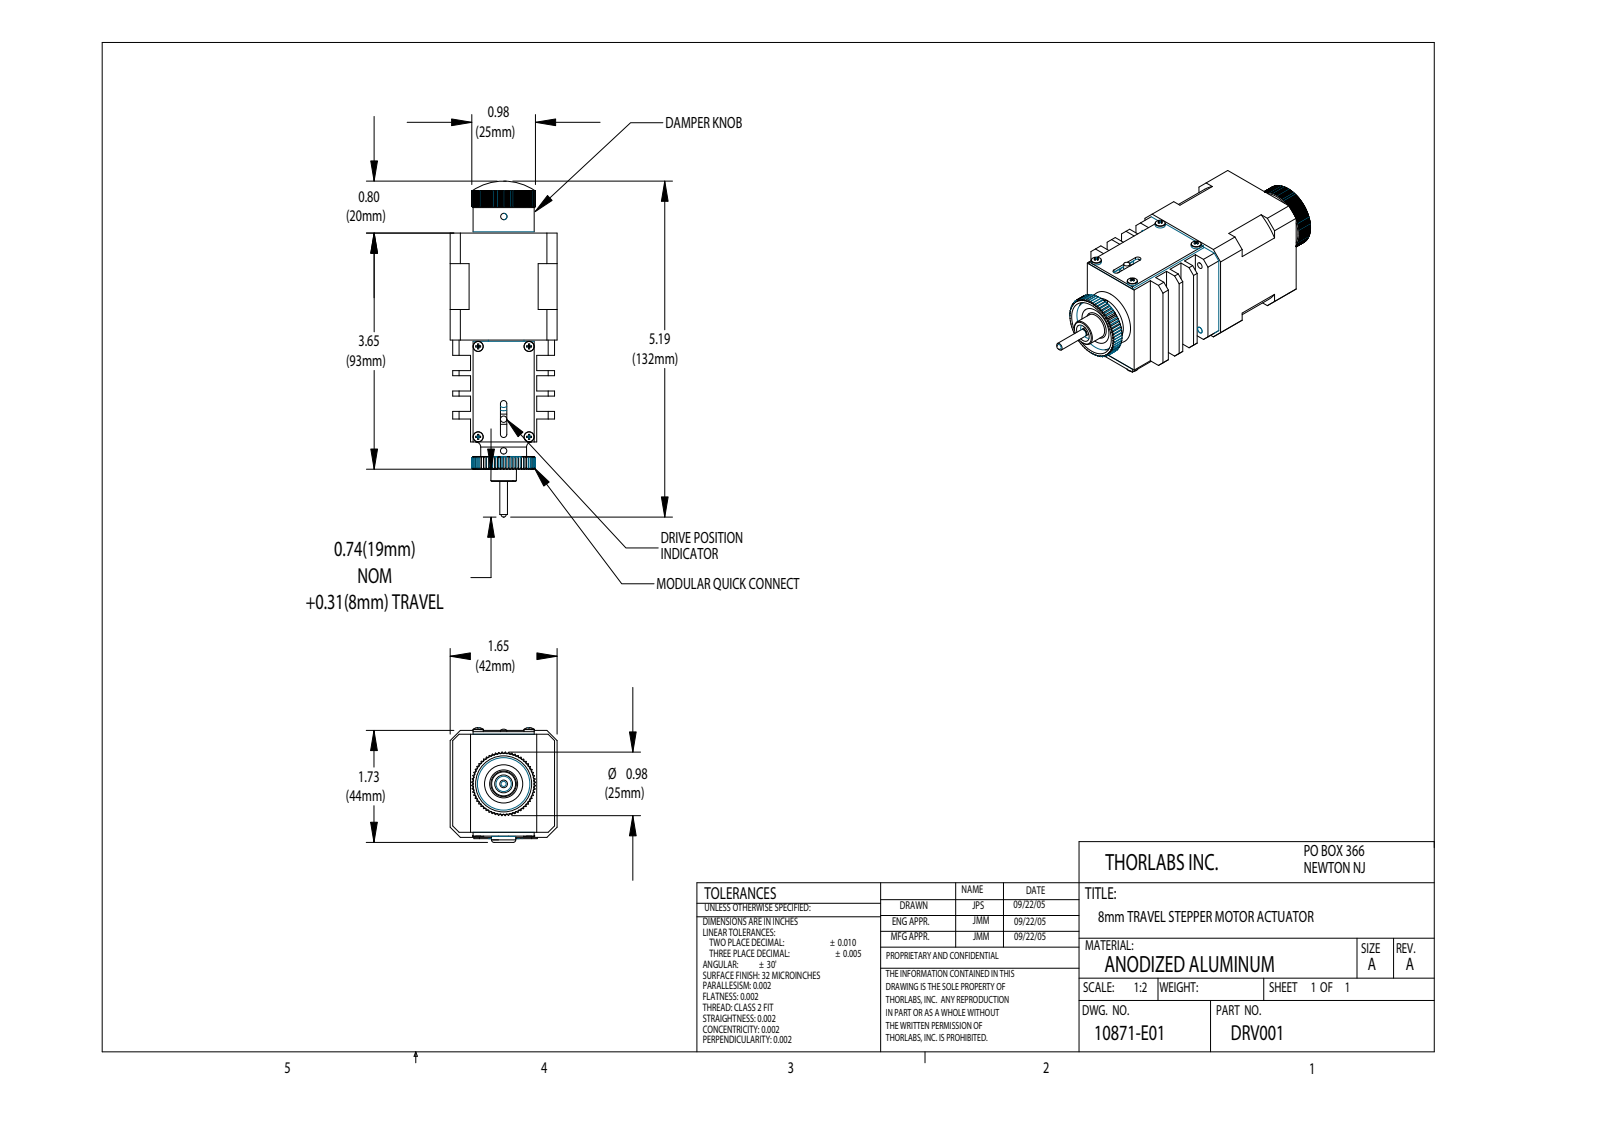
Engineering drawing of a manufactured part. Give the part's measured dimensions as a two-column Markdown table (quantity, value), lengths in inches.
| quantity | value |
| --- | --- |
| part name | 10871-E0W |
| STEP written by | SolidWorks 2007 (AUTOMOTIVE_DESIGN) |
| units | inches |
| bodies | 0 solids, 1417 faces (922 planar, 347 cylindrical, 148 other) |
| overall size | 5.193 × 1.773 × 1.654 |
| round holes (diameter × count) | 0.098 × 4, 0.256 × 4, 0.156 × 2, 0.276 × 1, 0.866 × 1 |
| round bosses / shafts (diameter × count) | 0.173 × 4, 0.157 × 4, 0.375 × 2, 0.945 × 1, 0.709 × 1, 0.394 × 1, 0.118 × 1, 0.098 × 1 |
| partial cylindrical surfaces (radius × count) | 0.049 × 2, 0.087 × 2, 0.236 × 2, 0.492 × 1, 0.984 × 1 |
| main face-to-face distances | 0.315, 1.654, 1.339, 1.575, 0.02, 0.236, 1.614, 0.039, 1.634, 0.079 |
| hole center spacings | 1.22, 0.863, 1.726, 0.472, 0.748 |
